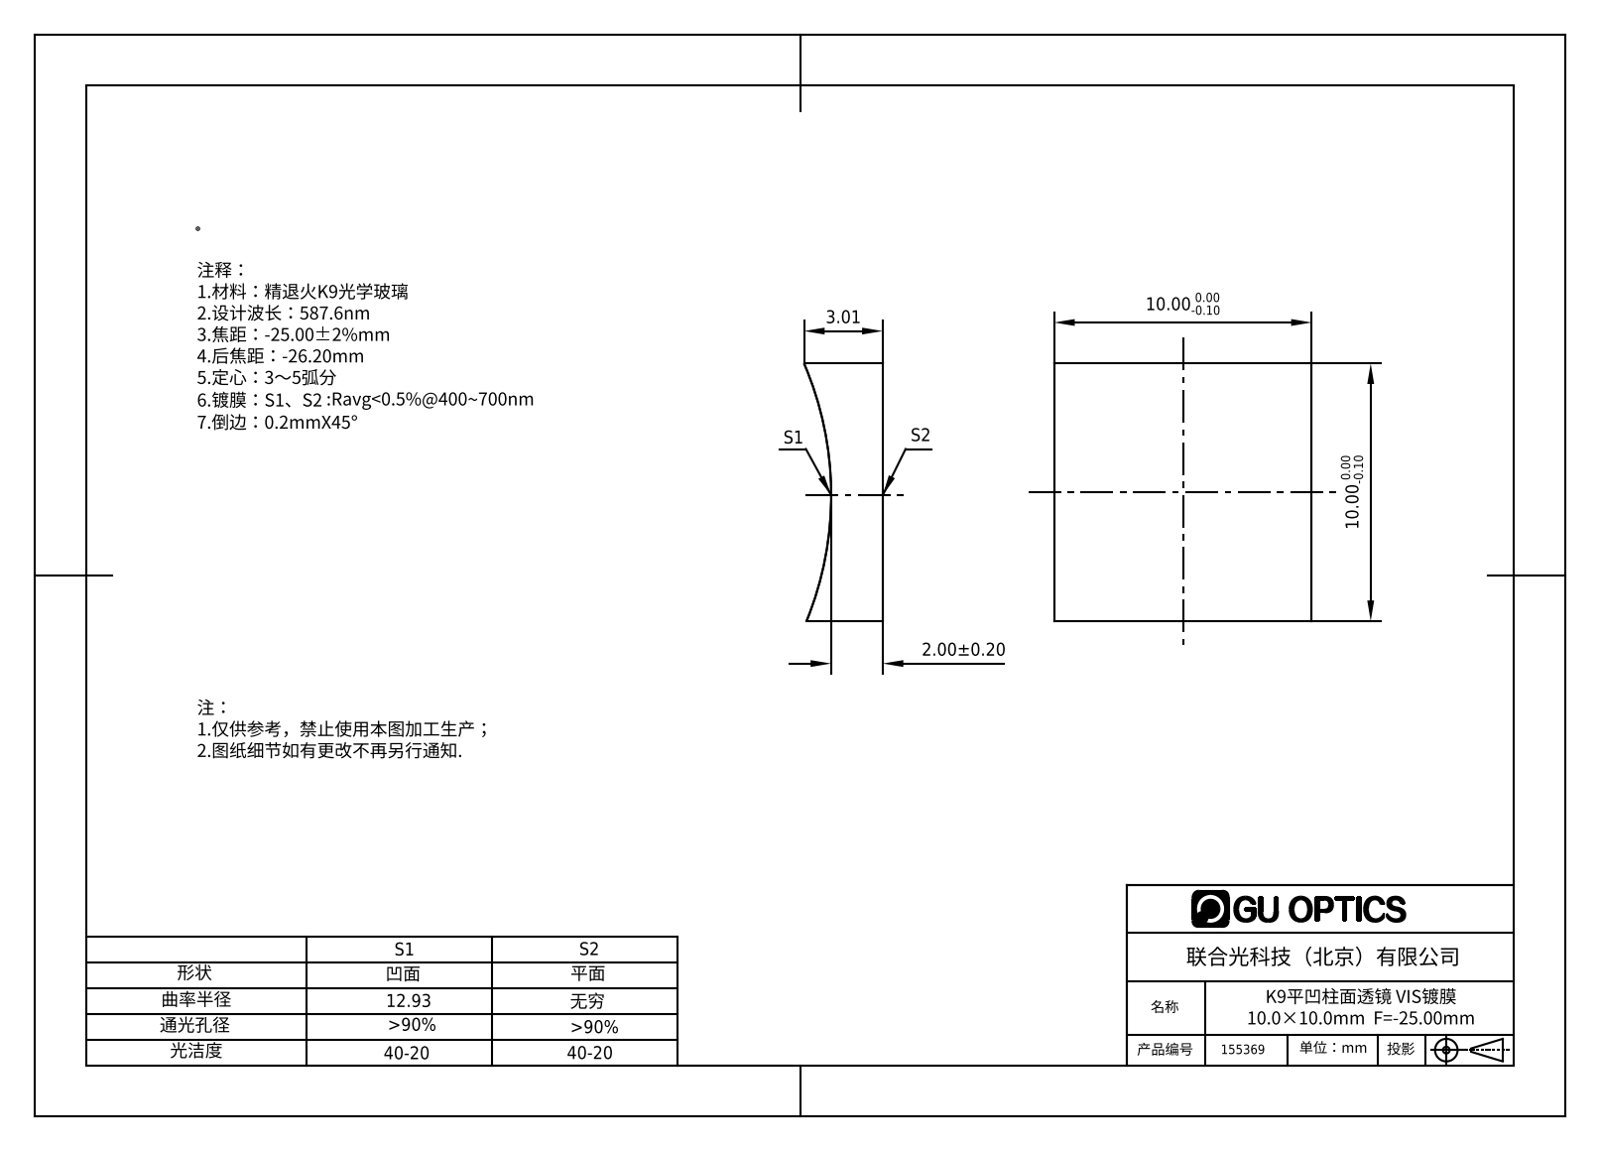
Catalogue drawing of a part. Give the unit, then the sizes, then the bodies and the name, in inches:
Units: inches
Overall size (bounding box): 0.394 × 0.394 × 0.12
Partial cylindrical surfaces — rounded edges, fillets, slot ends (radius × count): R0.509 ×1
Main face-to-face distances: 0.394
Volume: 0.014 in³ · Surface area: 0.479 in²
Bodies: 1 solid, 6 faces (5 planar, 1 cylindrical, 0 other)
Part name (STEP PRODUCT): 155336
STEP written by: SolidWorks 2016 (AUTOMOTIVE_DESIGN)
